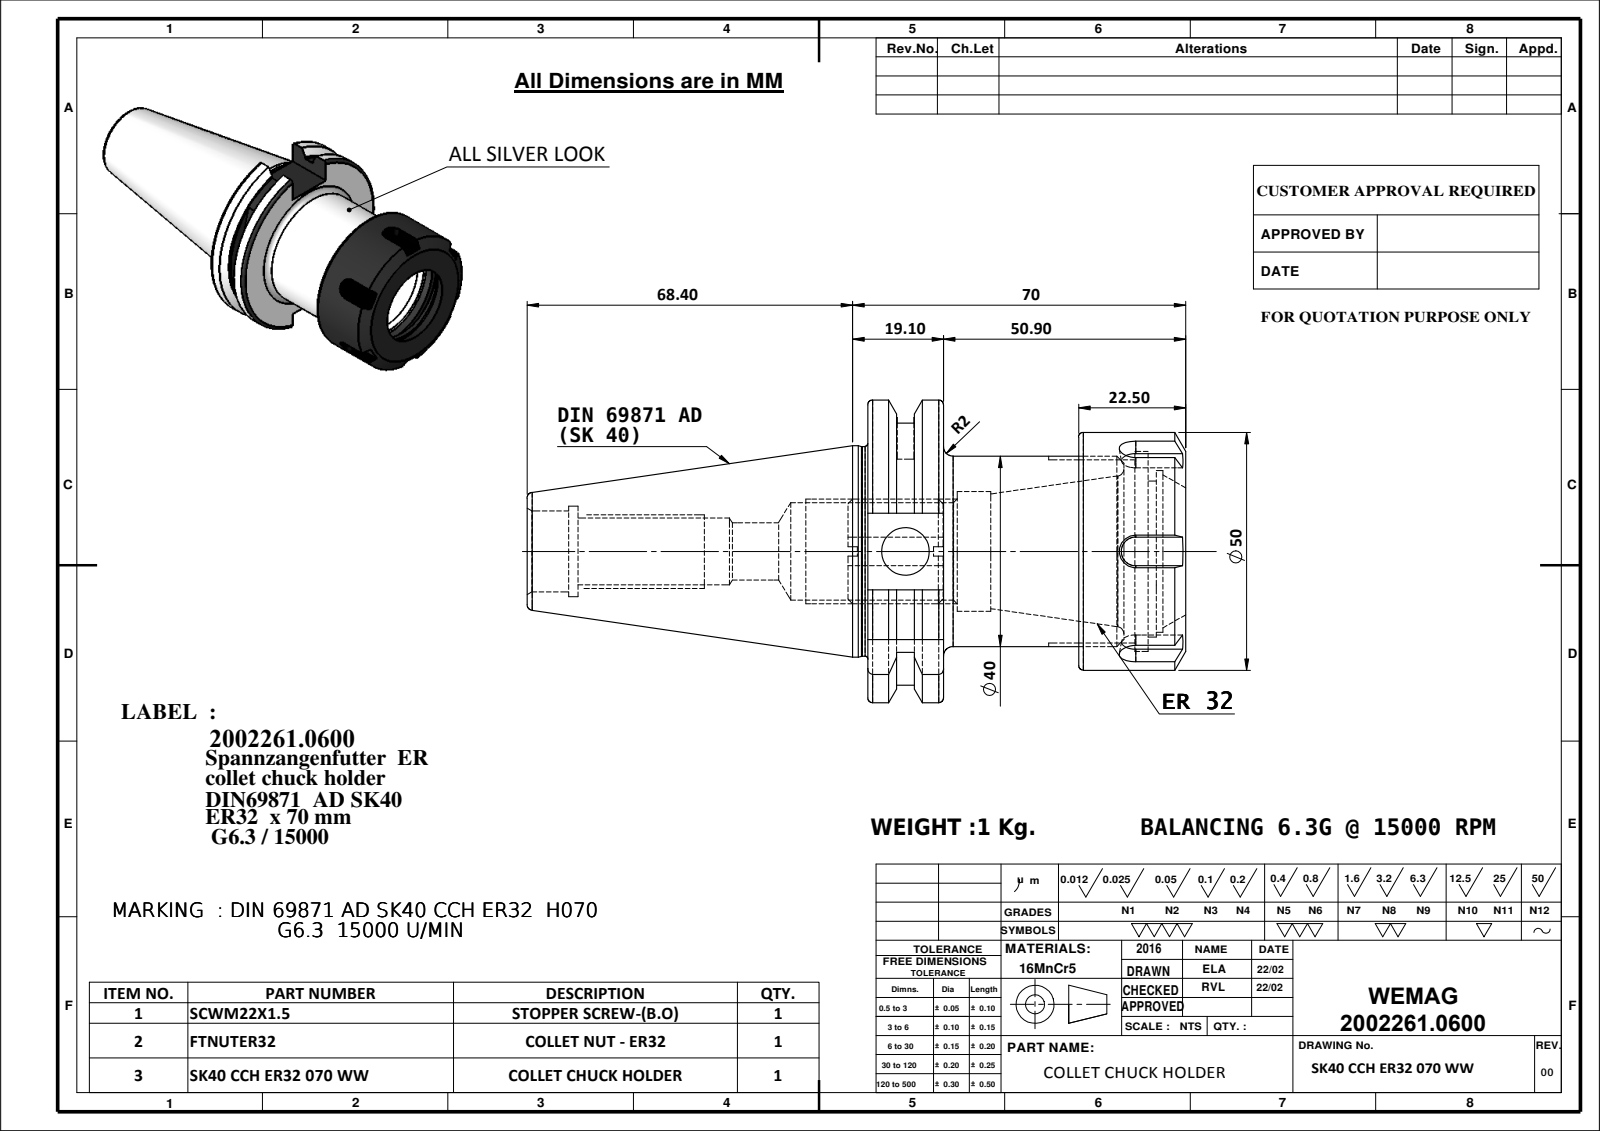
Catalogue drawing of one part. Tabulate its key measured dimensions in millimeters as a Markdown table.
| quantity | value |
| --- | --- |
| part name | FTSCWM22X150; SK40 CCH ER32 070 WW; FTNUTER32; 91406-ER132070 |
| STEP written by | SolidWorks 2009 (CONFIG_CONTROL_DESIGN) |
| units | millimeters |
| bodies | 3 solids, 177 faces (67 planar, 46 cylindrical, 64 other) |
| overall size | 138.4 × 63.55 × 61.48 |
| volume | 144 459 mm³ |
| surface area | 40 548 mm² |
| round holes (diameter × count) | 6 × 1, 10 × 1, 12 × 1, 14 × 1, 17 × 1, 19 × 1, 20.5 × 1, 25.2 × 1, 32.8 × 1, 34 × 1, 38.5 × 1, 42 × 1 |
| round bosses / shafts (diameter × count) | 50 × 1, 44.45 × 1, 44.05 × 1, 40 × 1, 22 × 1 |
| partial cylindrical surfaces (radius × count) | 28.12 × 1, 31.77 × 1 |
| main face-to-face distances | 15.9, 66.8, 50.9, 44.3, 28.4, 22.5, 58.9, 43, 14.6, 7.9 |
| hole center spacings | 1.6 |
